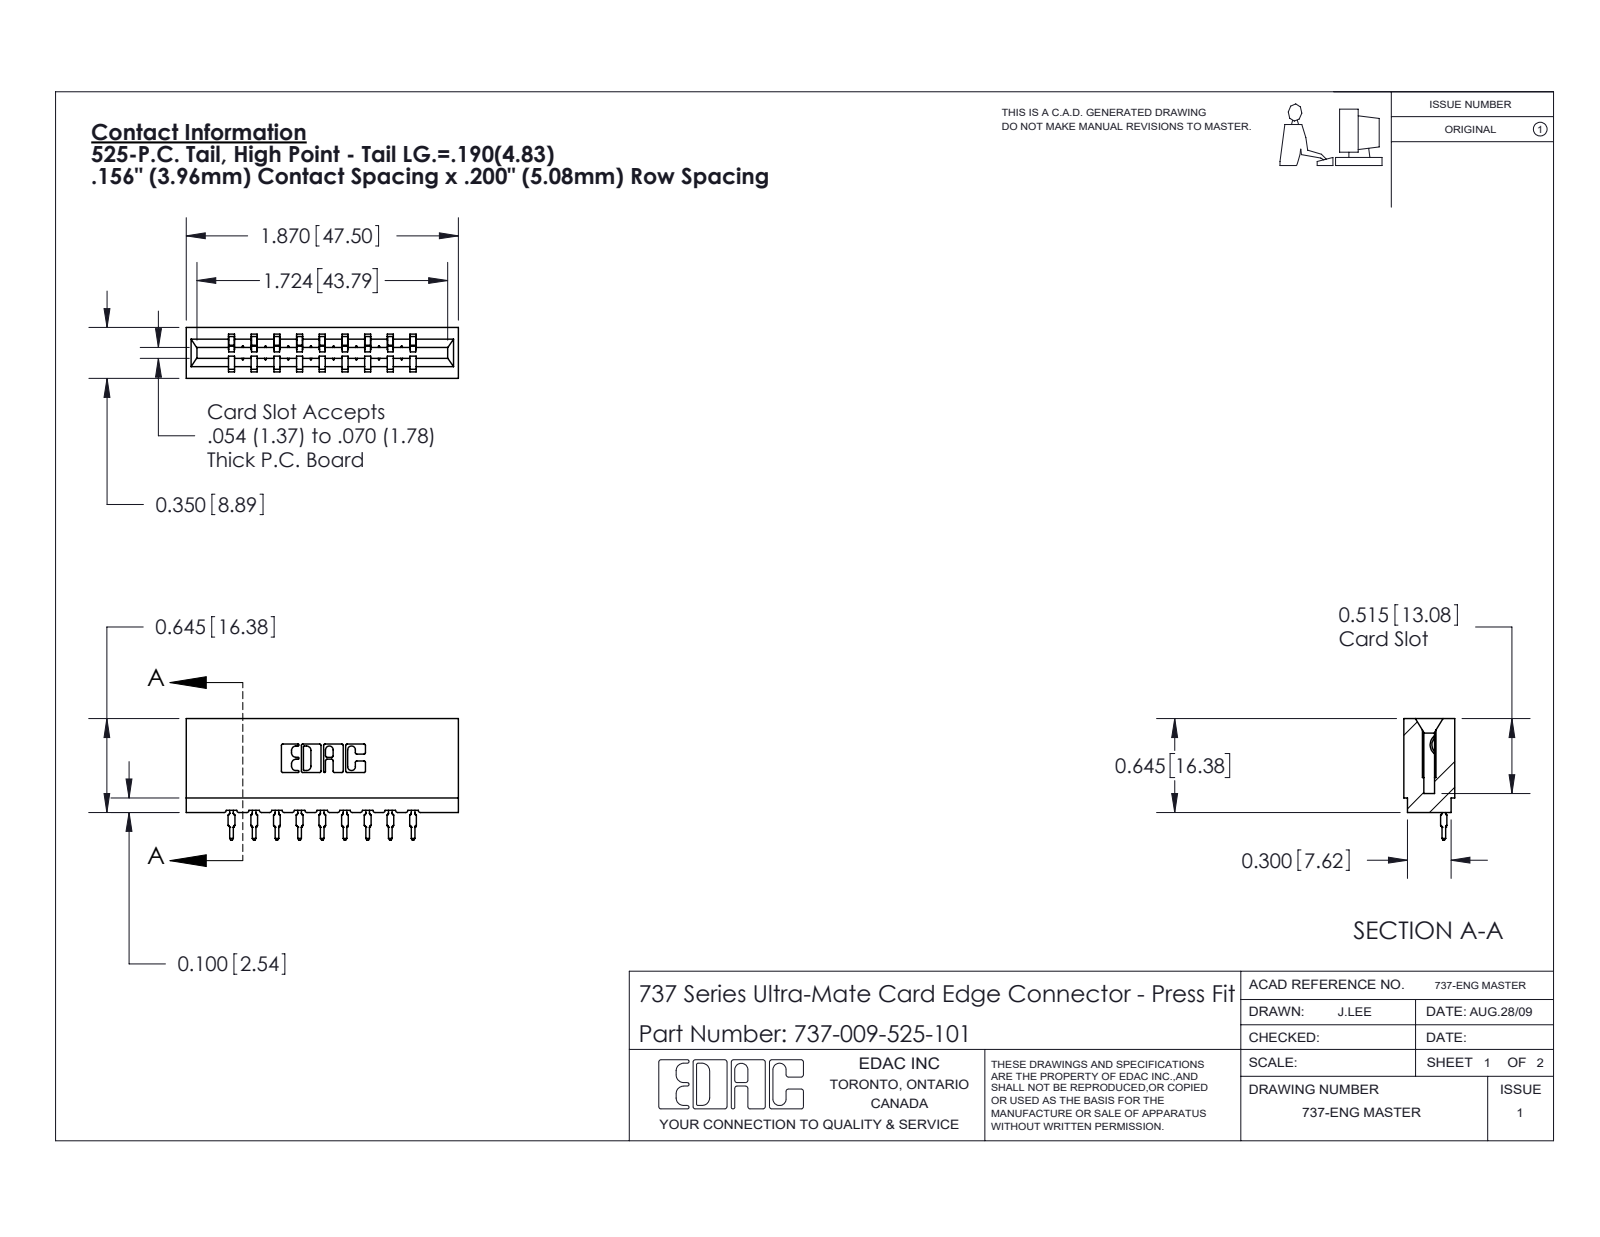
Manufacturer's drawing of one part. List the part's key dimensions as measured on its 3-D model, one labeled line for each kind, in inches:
Part name (STEP PRODUCT): 737-009-525-101; 745-292-001_525; 737 Part_Insulator Option - 01
STEP written by: SolidWorks 2020 (CONFIG_CONTROL_DESIGN)
Units: inches
Bodies: 10 solids, 1111 faces (666 planar, 211 cylindrical, 234 other)
Overall size (bounding box): 1.87 × 0.836 × 0.35
Volume: 0.294 in³ · Surface area: 9.039 in²
Partial cylindrical surfaces — rounded edges, fillets, slot ends (radius × count): R0.01 ×22, R0.015 ×18, R0.021 ×18, R0.007 ×6, R0.031 ×6, R0.005 ×4, R0.011 ×4, R0.026 ×3
Main face-to-face distances: 0.156, 0.138, 0.212, 0.624, 0.35, 0.312, 0.468, 0.354, 0.78, 0.198
